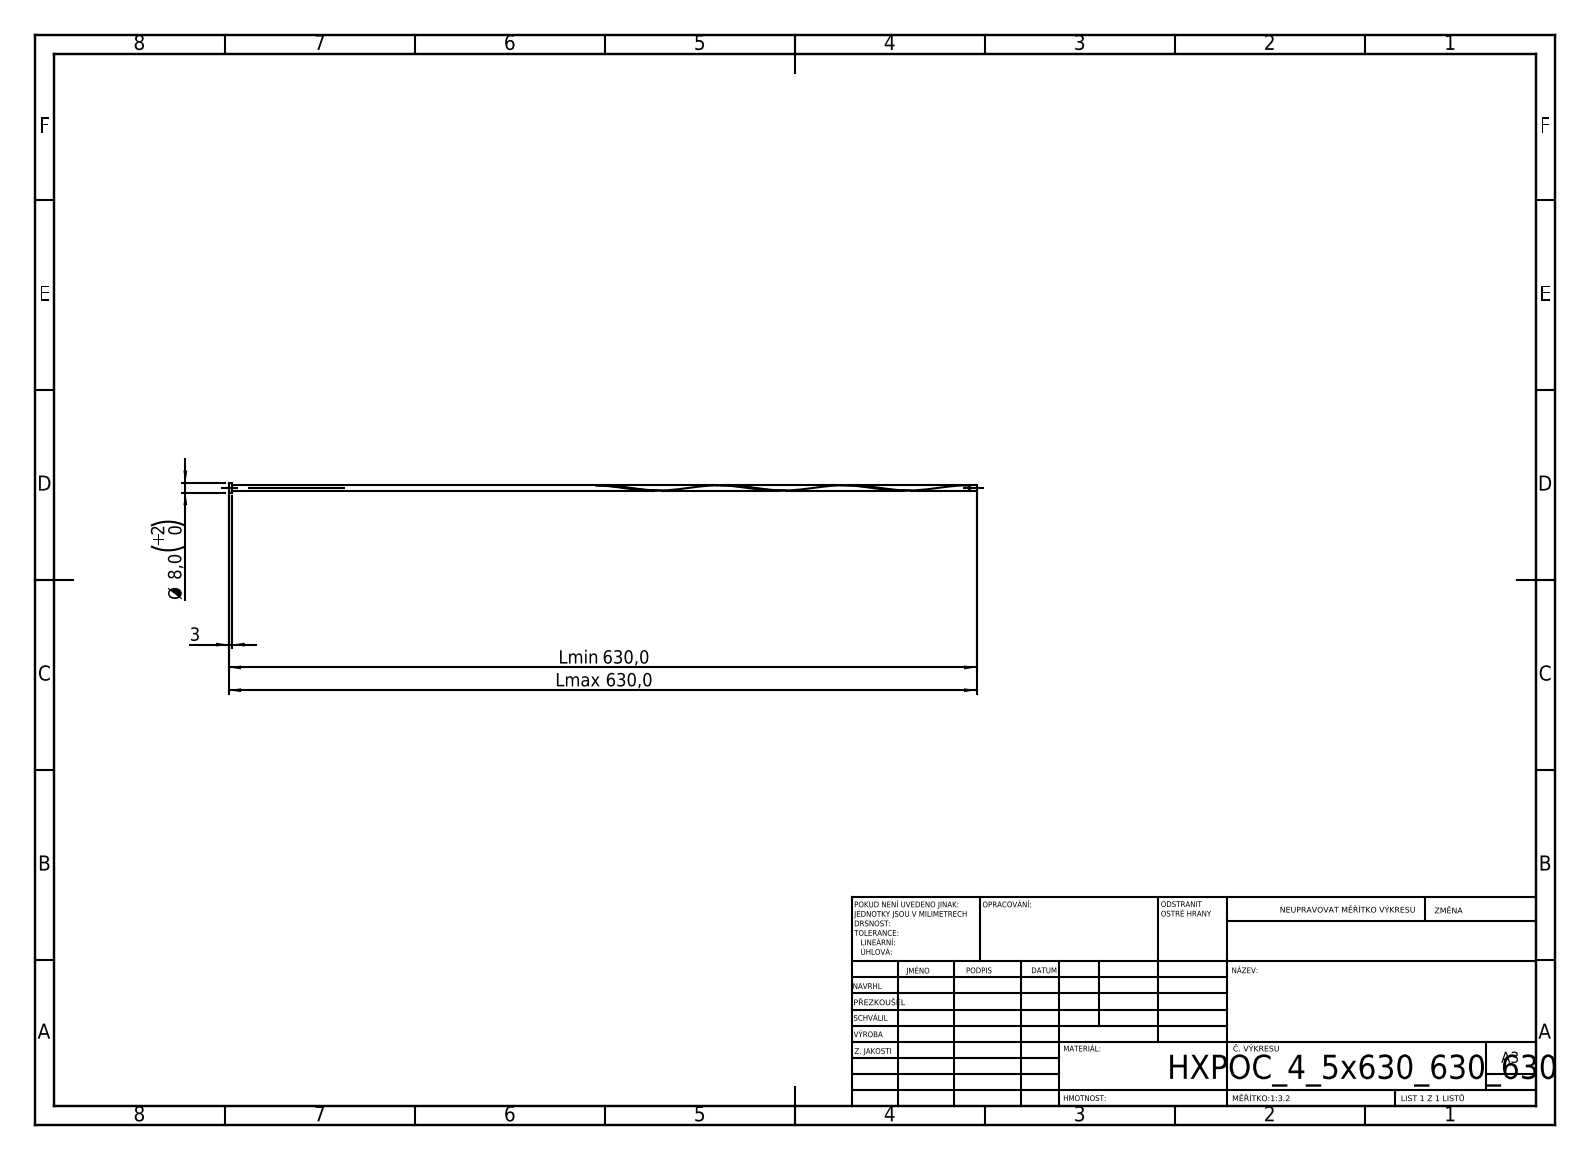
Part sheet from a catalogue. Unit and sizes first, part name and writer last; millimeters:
Units: millimetres
Overall size (bounding box): 630 × 8 × 8
Round bosses / shafts (diameter × count): ⌀8 ×1, ⌀4.5 ×1, ⌀3.6 ×1
Main face-to-face distances: 3, 630, 627, 624.86, 621.86, 5.14, 623.96, 620.96, 0.9, 6.04
Volume: 12 248 mm³ · Surface area: 12 152 mm²
Bodies: 1 solid, 16 faces (6 planar, 9 cylindrical, 1 other)
STEP written by: SolidWorks 2019 (CONFIG_CONTROL_DESIGN)
